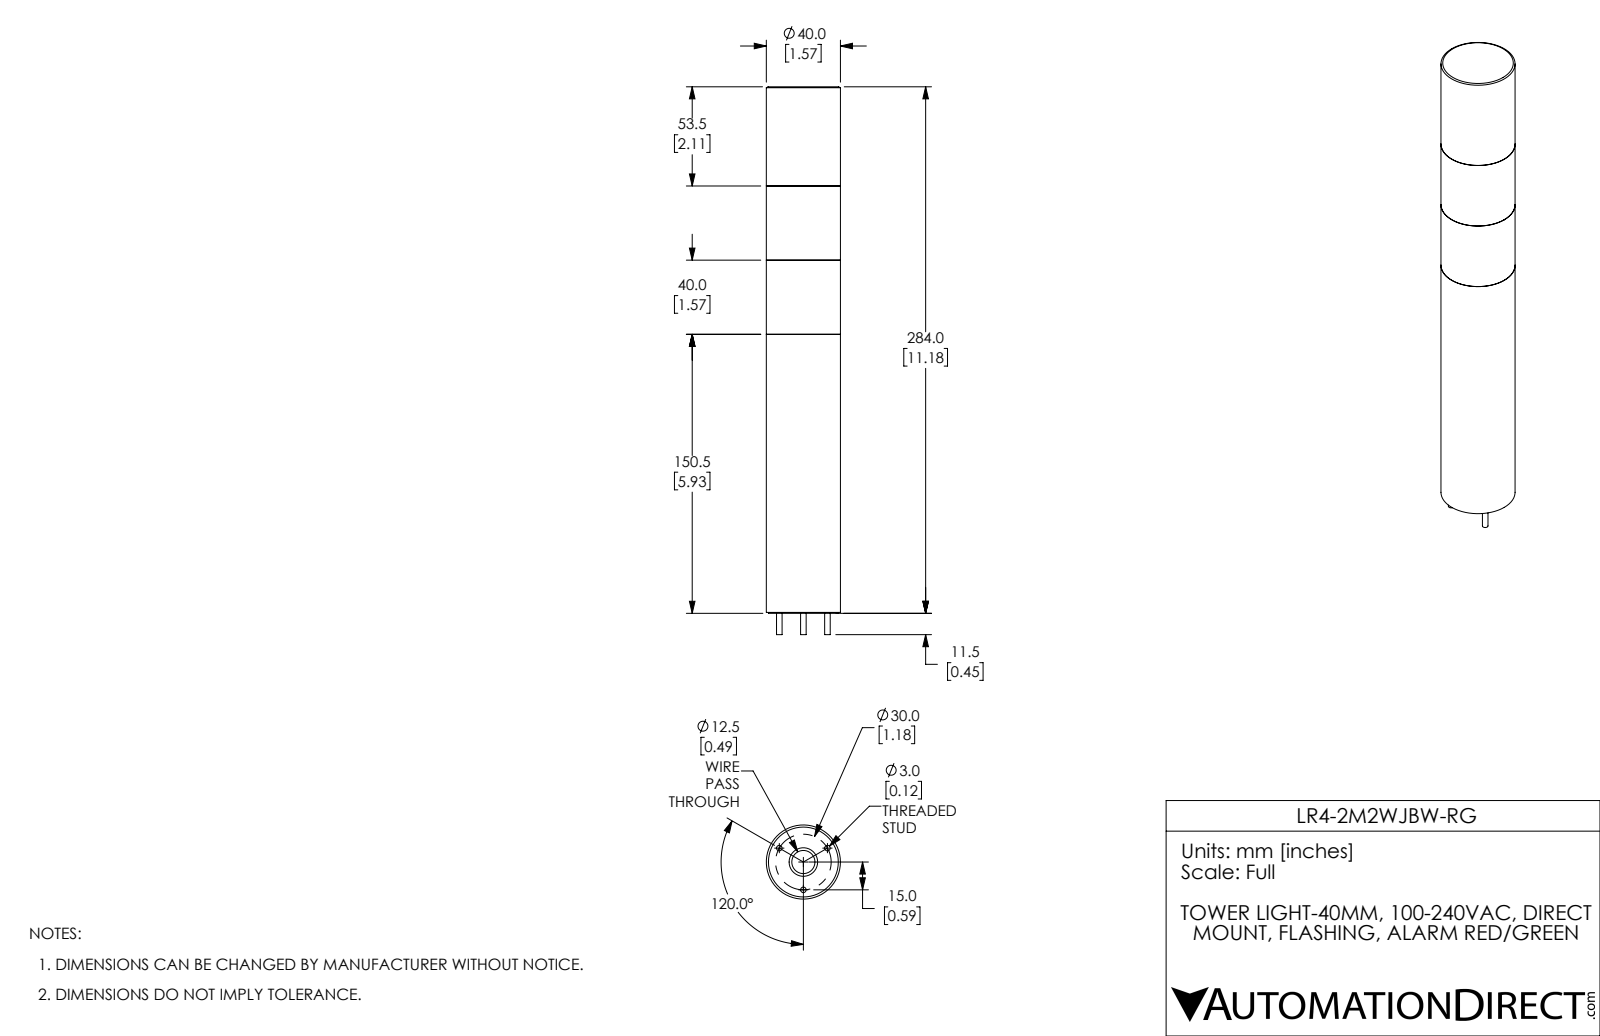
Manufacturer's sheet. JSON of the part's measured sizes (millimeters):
{"part_name": "LR4-2M2WJBW-RG", "step_written_by": "SolidWorks 2017 (AUTOMOTIVE_DESIGN)", "units": "millimeters", "bodies": {"solids": 4, "faces": 69, "planar": 25, "cylindrical": 42, "other": 2}, "overall_size": [295.5, 40, 40], "volume_mm3": 354800, "surface_area_mm2": 53250, "round_holes": [[12.5, 1], [15.4, 1], [35.2, 1], [37.2, 1], [37.5, 1]], "round_bosses_or_shafts": [[3, 3], [40, 1], [37.7, 1], [37.1, 1], [34.7, 1]], "face_to_face_distances": [40, 80, 43.2, 83.2, 123.2, 80.3, 40.3, 42.9, 10.3, 160.8]}
